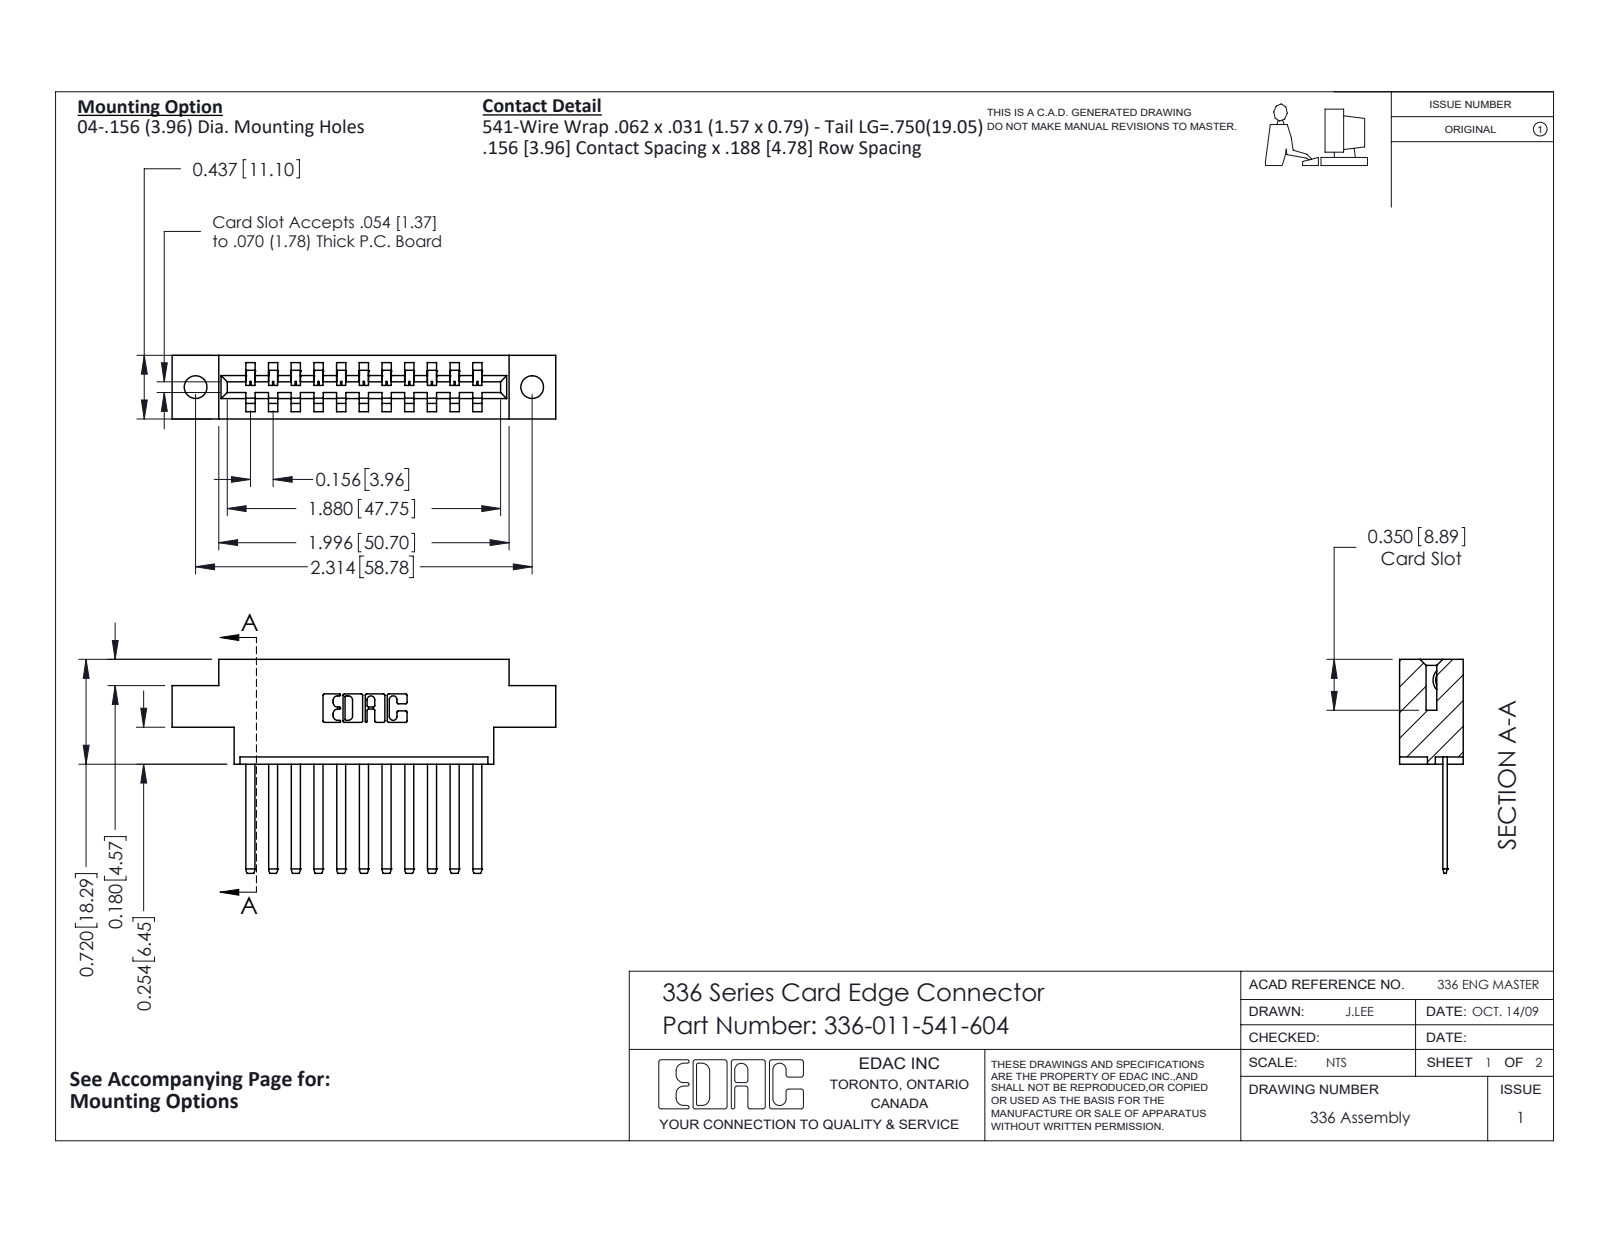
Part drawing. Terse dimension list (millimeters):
name: 336-290-001_336-290-541; 336-011-541-604; 336 Part_Offset - .156 Dia - TH
written by: SolidWorks 2020 (CONFIG_CONTROL_DESIGN)
unit: mm
bodies: 12 solids, 668 faces (448 planar, 220 cylindrical, 0 other)
size: 67 × 37.3 × 11.1
volume: 8 770 mm³; area: 9 032 mm²
holes: 2× ⌀4
rounds: 22× R0.1, 22× R0.3, 22× R1.4, 6× R0.2, 6× R0.8, 3× R0.7, 2× R0.6, 2× R1
face distances: 11.1, 4, 11.9, 15.8, 7.9, 19.8, 4.6, 6.5, 7.9, 10.3
hole spacings: 58.8
